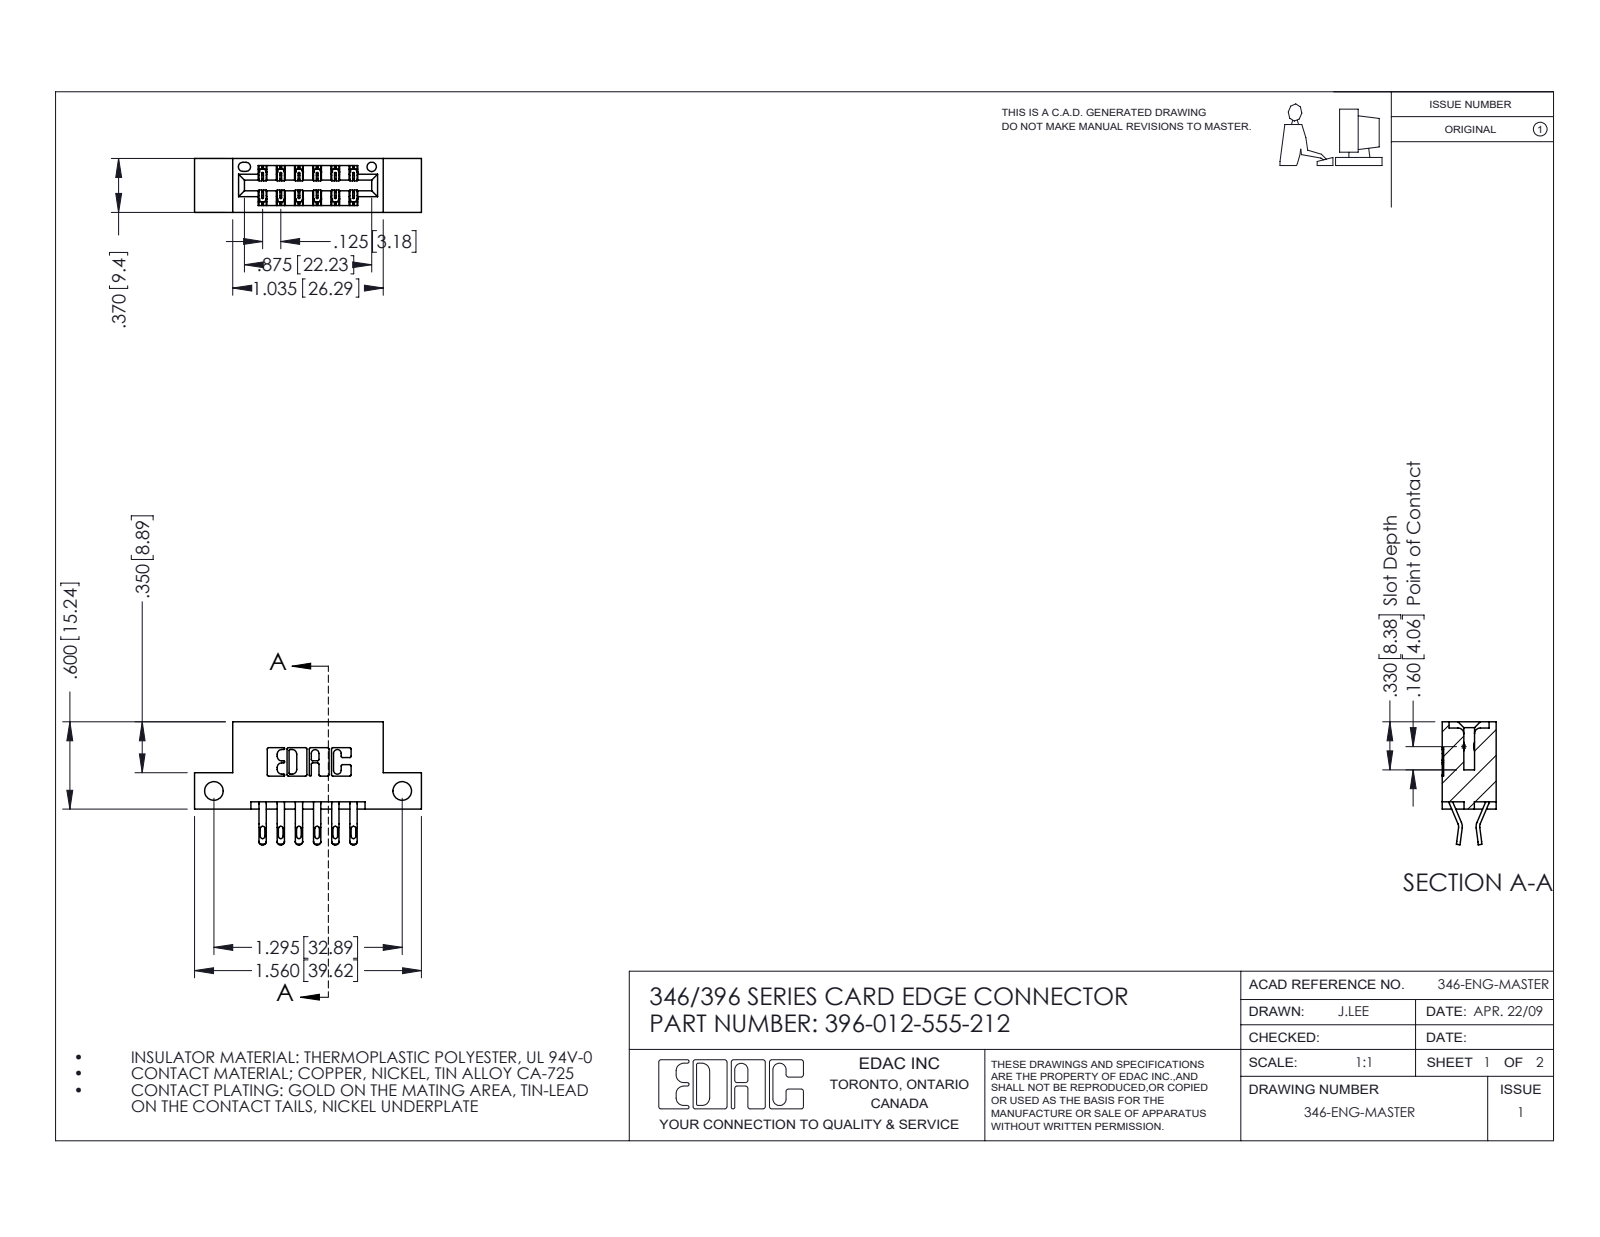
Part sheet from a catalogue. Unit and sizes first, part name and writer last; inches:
Units: inches
Overall size (bounding box): 1.56 × 0.845 × 0.37
Round holes (diameter × count): ⌀0.128 ×2, ⌀0.064 ×1
Partial cylindrical surfaces — rounded edges, fillets, slot ends (radius × count): R0.016 ×24, R0.02 ×24, R0.01 ×22, R0.006 ×18, R0.007 ×6, R0.031 ×6, R0.026 ×3, R0.01 ×2
Main face-to-face distances: 0.25, 0.37, 0.048, 0.322, 0.125, 0.148, 0.222, 0.1, 0.174, 0.025
Hole centre spacings: 1.295
Volume: 0.216 in³ · Surface area: 6.627 in²
Bodies: 13 solids, 818 faces (472 planar, 346 cylindrical, 0 other)
Part name (STEP PRODUCT): 346 Part_Flush Mounting Lugs - Side Mount; 345-292-001_555 Tail; 396-012-555-212
STEP written by: SolidWorks 2016 (CONFIG_CONTROL_DESIGN)
